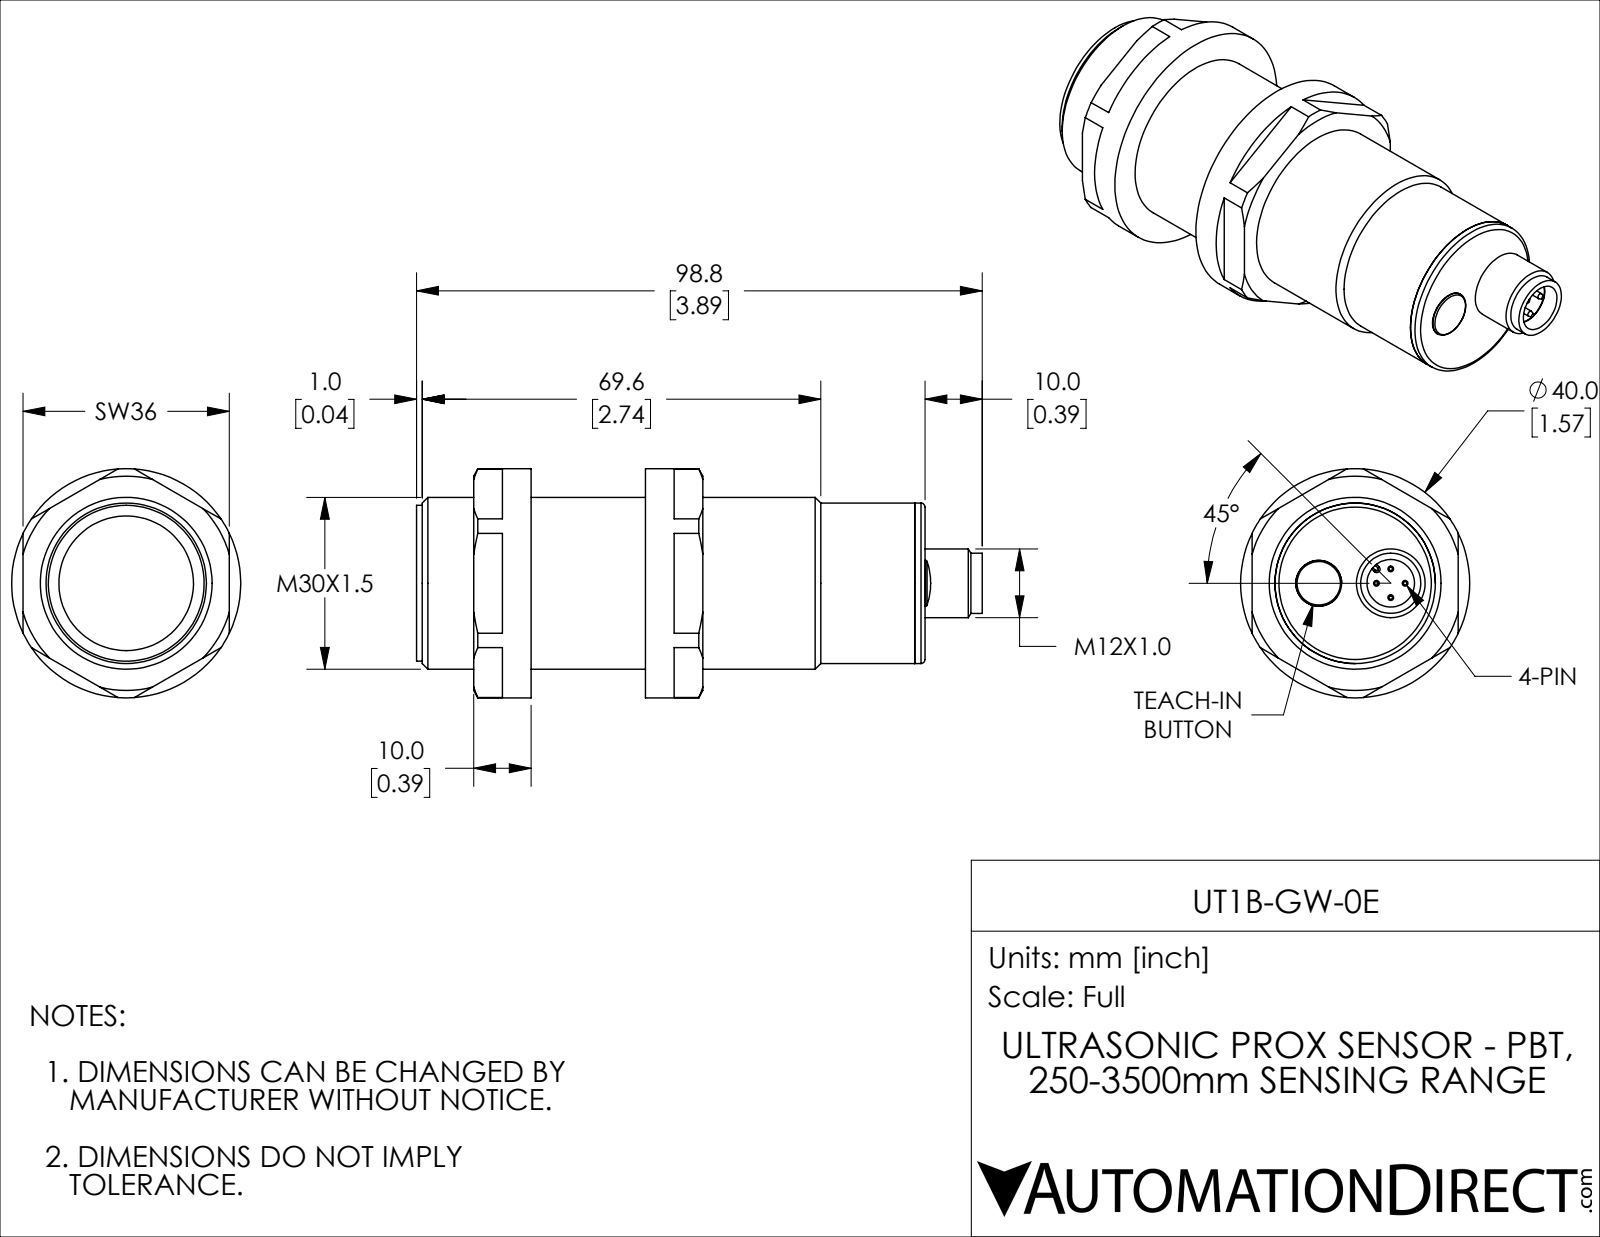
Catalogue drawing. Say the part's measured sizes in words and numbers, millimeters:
The part is named "UT1B-GW-0E". Its 3-D file was written by "SolidWorks 2018 (AUTOMOTIVE_DESIGN)". It is 7 solids with 158 faces: 58 planar, 53 cylindrical and 47 other. Overall it measures 98.8 by 40 by 40 millimeters. Its volume is 71 077 cubic millimeters and its surface area 19 881 square millimeters. Round holes: 4 of diameter 1.8, 1 of diameter 8, 1 of diameter 8.3, 1 of diameter 9.45, 1 of diameter 23.5, 1 of diameter 30. Round bosses or shafts: 4 of diameter 1, 1 of diameter 40, 1 of diameter 28, 1 of diameter 27.2, 1 of diameter 12, 1 of diameter 10.5, 1 of diameter 9.25. Partial cylindrical surfaces (rounded edges, fillets, slot ends): 2 of radius 0.3, 1 of radius 0.6. The main face-to-face distances are 86, 10, 30, 20, 5, 40, 47, 39, 19, 67. The hole center spacings are 2.5, 3.54, 5, 6.7, 12.83, 3.72, 6.22, 6.36.
